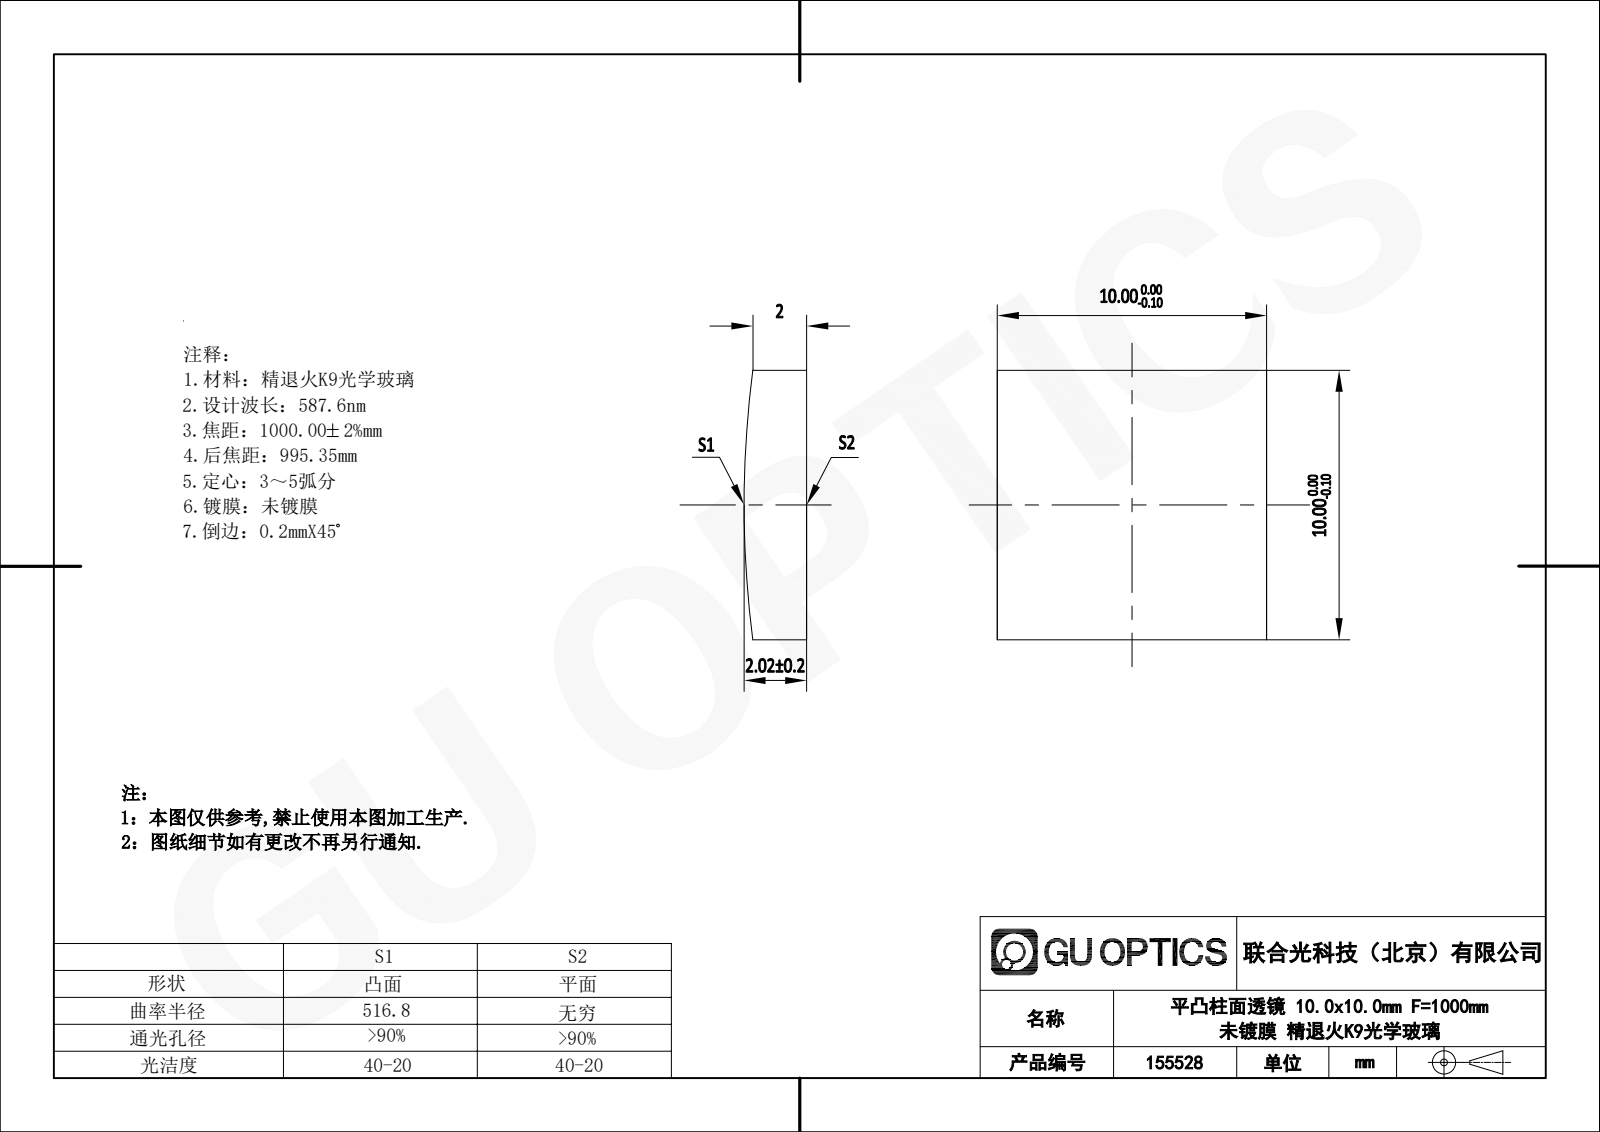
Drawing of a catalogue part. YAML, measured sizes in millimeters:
part_name: "155528"
step_written_by: "SolidWorks 2020 (CONFIG_CONTROL_DESIGN)"
units: millimeters
bodies: {solids: 1, faces: 7, planar: 5, cylindrical: 2, other: 0}
overall_size: [10, 10, 2.02]
volume: 202
surface_area: 280
partial_cylinders:
  - {radius: 516.8, count: 1}
face_to_face_distances: [10]
